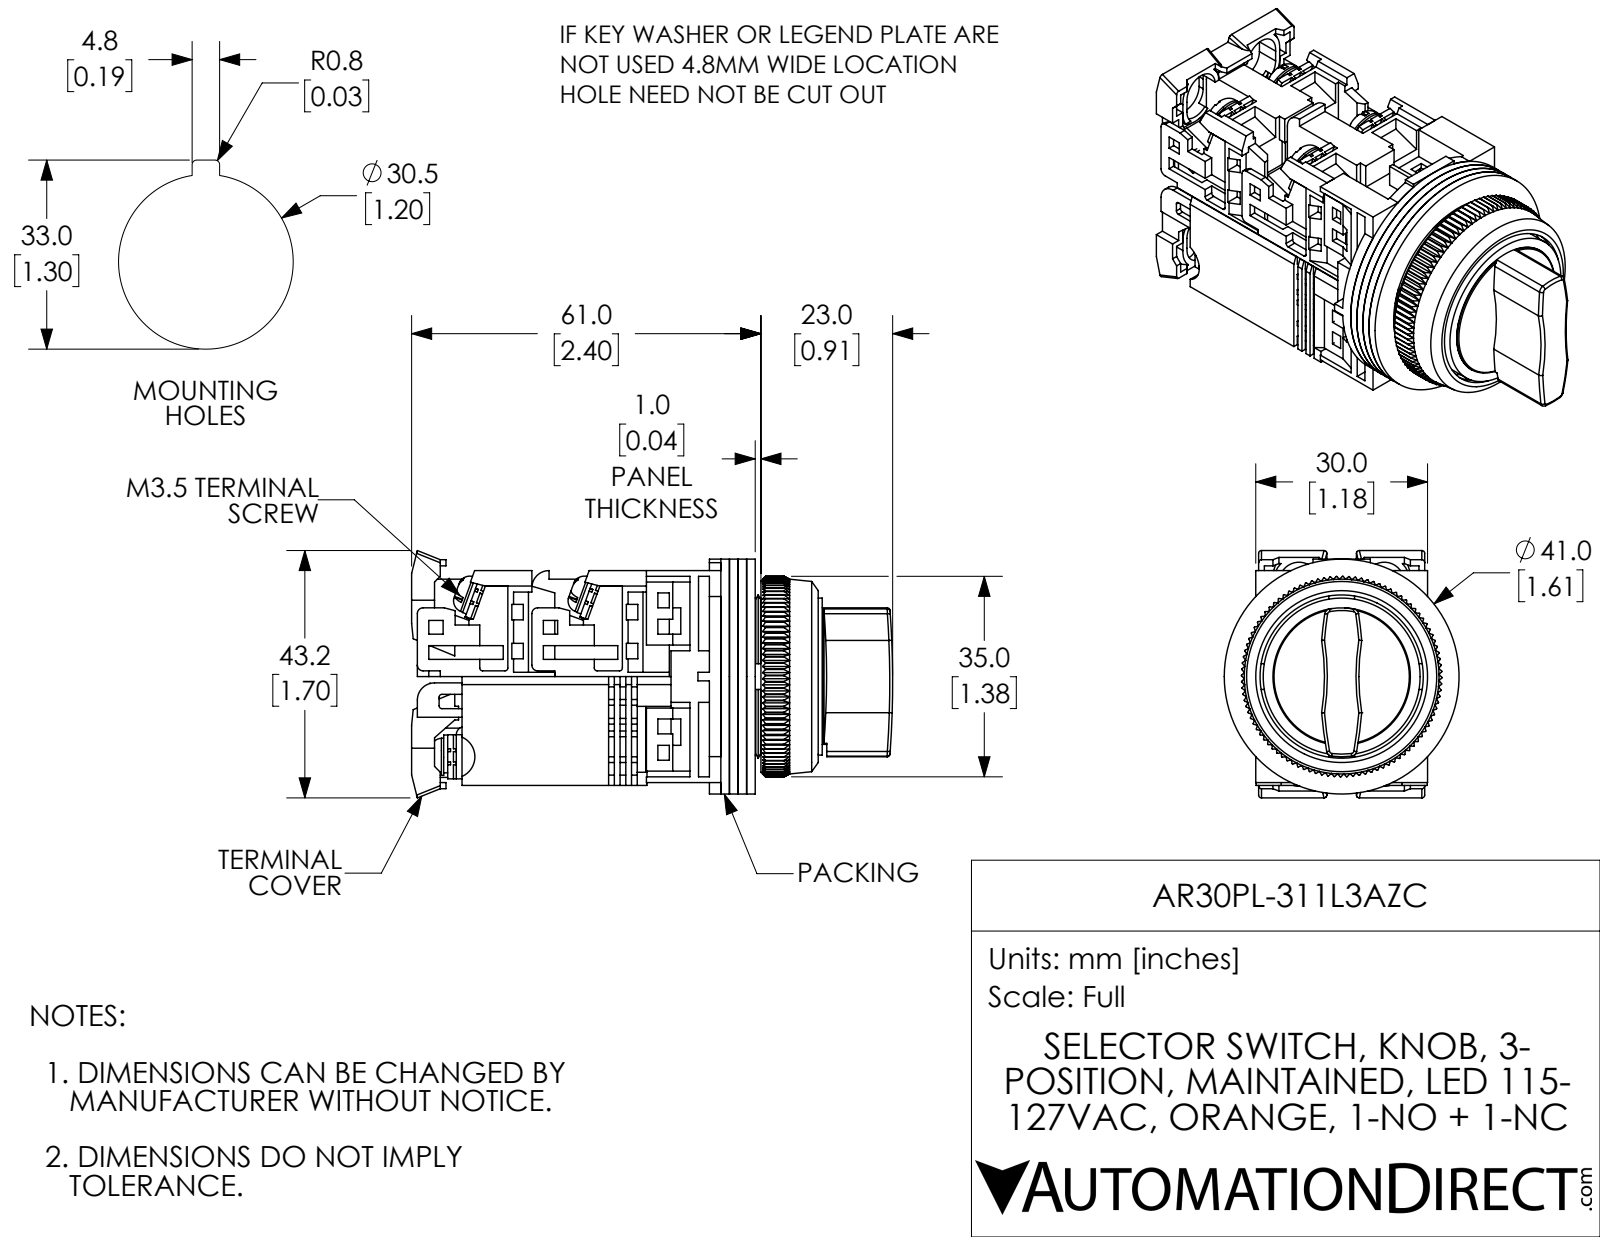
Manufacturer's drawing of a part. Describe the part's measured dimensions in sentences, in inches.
The part is named "AR30PL-311L3AZC". Its 3-D file was written by "SolidWorks 2017 (AUTOMOTIVE_DESIGN)". It is 34 solids with 2724 faces: 2033 planar, 354 cylindrical and 337 other. Overall it measures 3.307 by 1.7 by 1.614 inches. Its volume is 3.442 cubic inches and its surface area 70.72 square inches. Round holes: 8 of diameter 0.138, 6 of diameter 0.142, 3 of diameter 0.118, 1 of diameter 0.472, 1 of diameter 0.709, 1 of diameter 0.768, 1 of diameter 0.827, 1 of diameter 1.122, 1 of diameter 1.181, 1 of diameter 1.252. Round bosses or shafts: 6 of diameter 0.26, 4 of diameter 0.138, 2 of diameter 0.063, 1 of diameter 1.614, 1 of diameter 1.15, 1 of diameter 1.079, 1 of diameter 0.945, 1 of diameter 0.886. Partial cylindrical surfaces (rounded edges, fillets, slot ends): 25 of radius 0.059, 15 of radius 0.02, 8 of radius 0.039, 4 of radius 0.138, 4 of radius 0.177, 3 of radius 0.118, 2 of radius 1.575, 2 of radius 2.953. The main face-to-face distances are 0.059, 0.118, 0.177, 0.039, 0.748, 0.079, 0.787, 0.063, 0.689, 0.197. The hole center spacings are 0.579, 0.269, 0.638, 0.297, 0.624, 0.02, 0.302, 0.583.
